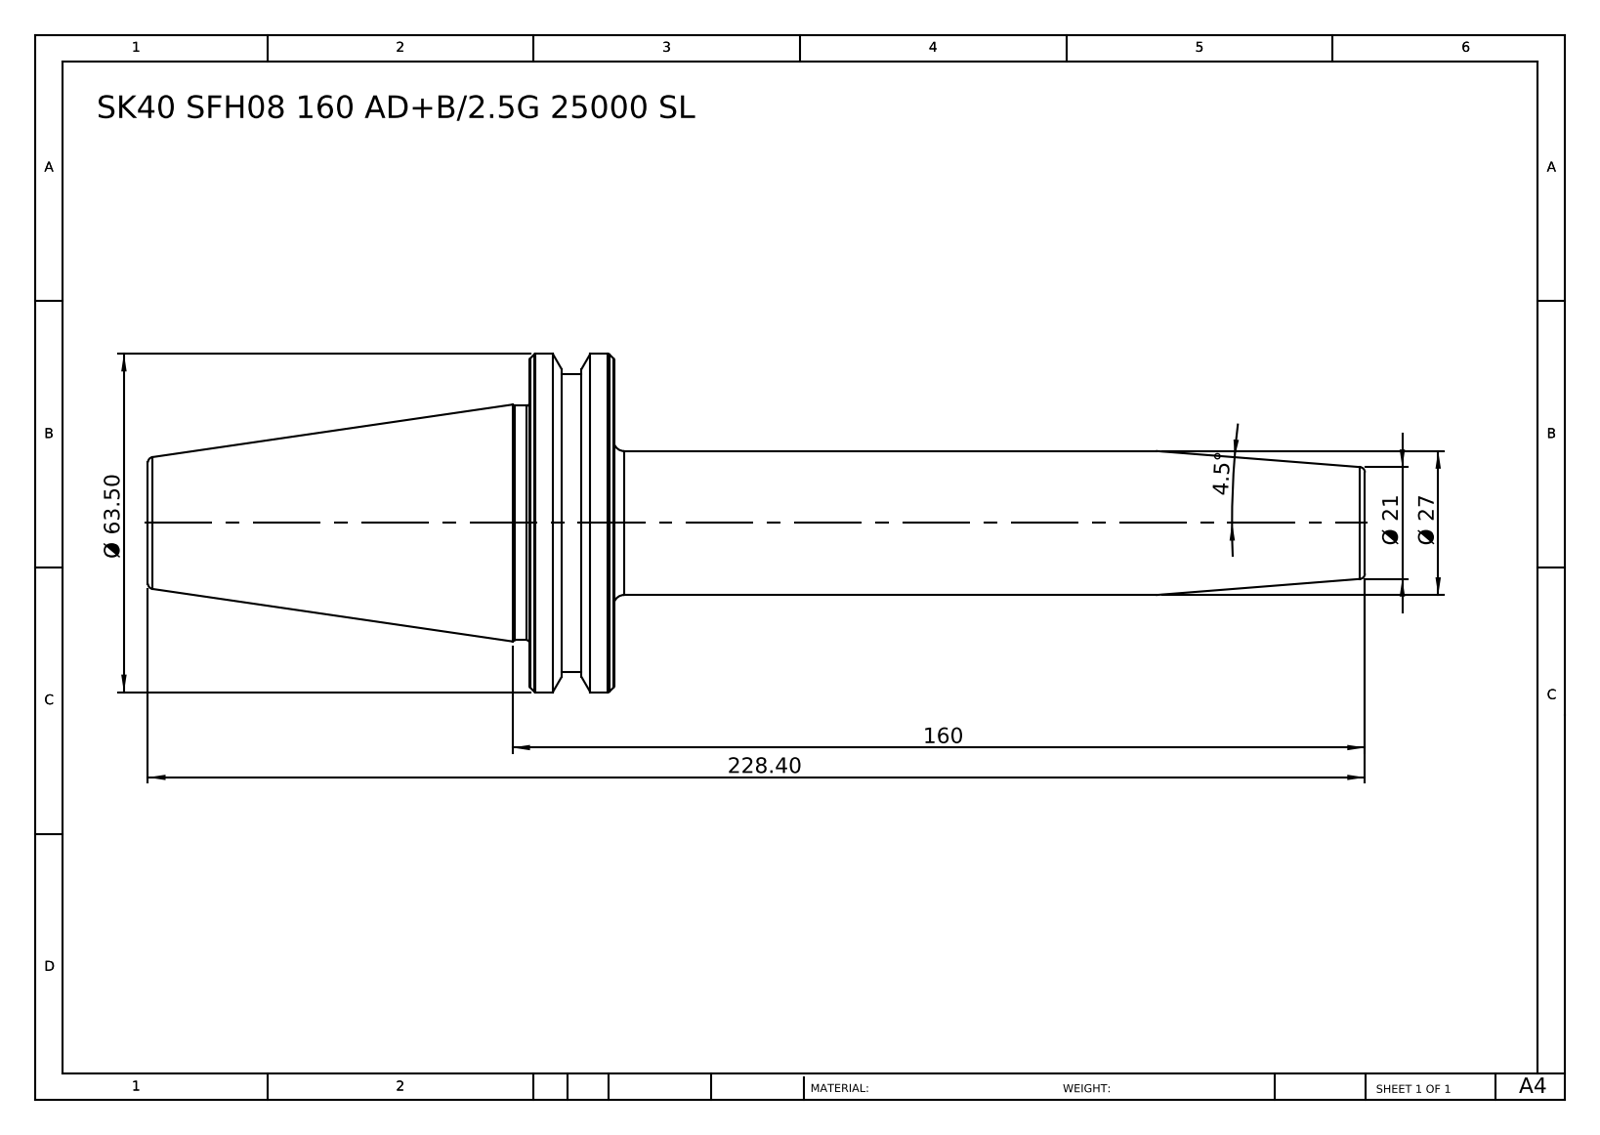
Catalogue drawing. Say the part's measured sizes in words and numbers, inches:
The part is named "SK40 SFH08 160 AD+B-2.5G 25000 SL". Its 3-D file was written by "SolidWorks 2014 (CONFIG_CONTROL_DESIGN)". It is 1 solid with 46 faces: 6 planar, 10 cylindrical and 30 other. Overall it measures 8.992 by 2.5 by 2.5 inches. Its volume is 11.78 cubic inches and its surface area 43.7 square inches. Round bosses or shafts: 1 of diameter 2.5, 1 of diameter 2.205, 1 of diameter 1.732, 1 of diameter 1.063. The main face-to-face distances are 0.626, 3.445, 2.819, 5.547, 6.173, 8.992, 5.787, 0.24, 0.386, 3.205.
